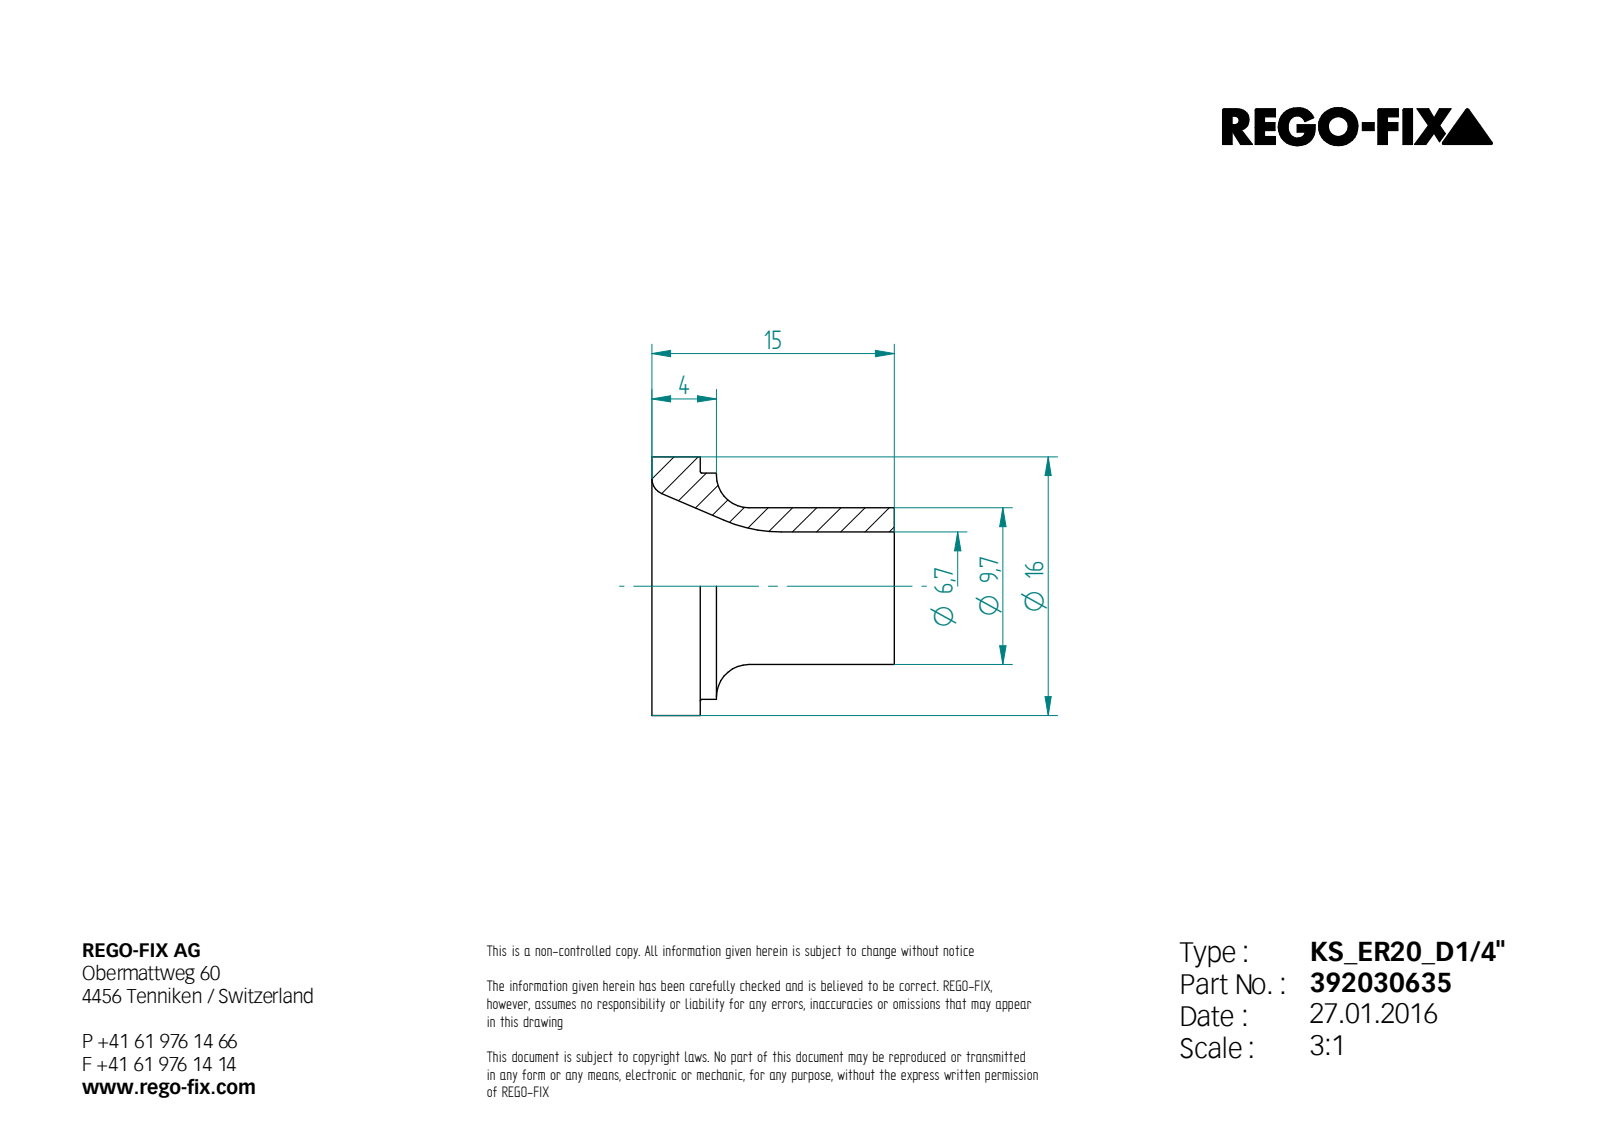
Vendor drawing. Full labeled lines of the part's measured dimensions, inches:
STEP written by: Unknown (AUTOMOTIVE_DESIGN)
Units: inches
Bodies: 1 solid, 13 faces (4 planar, 4 cylindrical, 5 other)
Overall size (bounding box): 0.63 × 0.63 × 0.591
Volume: 0.052 in³ · Surface area: 1.759 in²
Round holes (diameter × count): ⌀0.264 ×1
Round bosses / shafts (diameter × count): ⌀0.63 ×1, ⌀0.551 ×1, ⌀0.382 ×1
Main face-to-face distances: 0.118, 0.591, 0.472, 0.157, 0.039, 0.433
